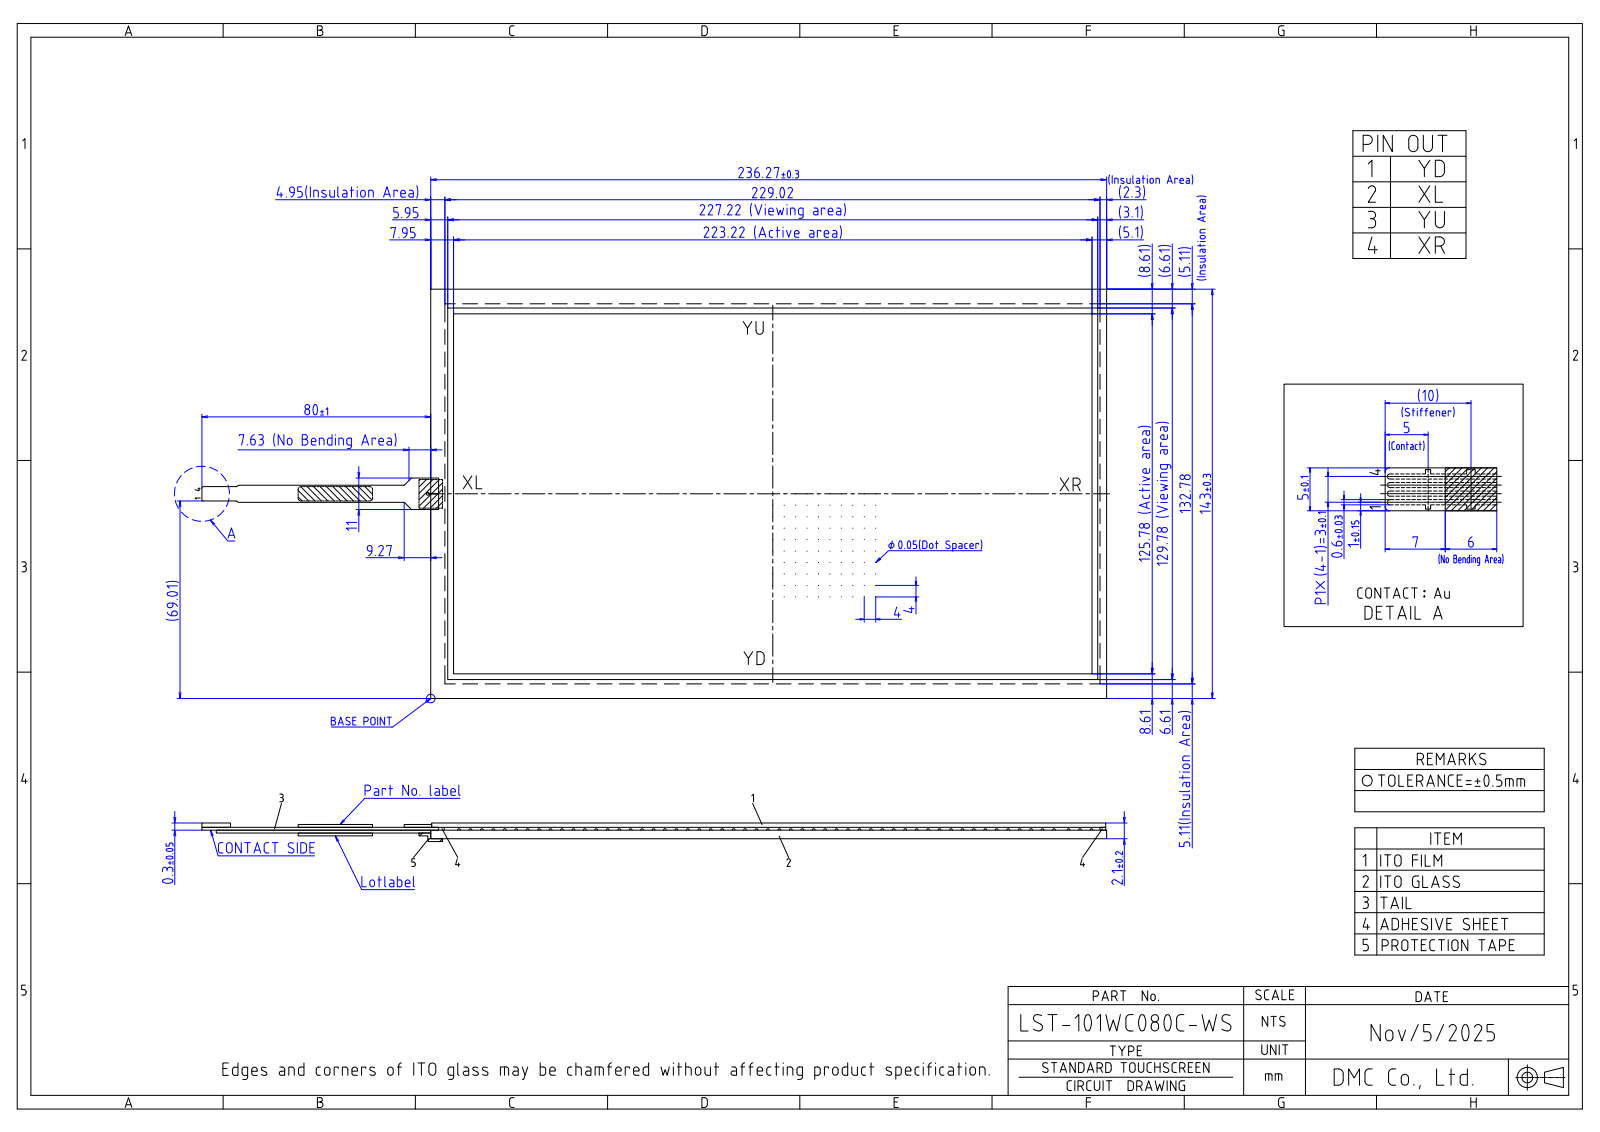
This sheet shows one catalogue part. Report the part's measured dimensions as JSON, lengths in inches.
{"part_name": "LST-101WC080C-WS (3Dデータ)", "step_written_by": "Autodesk Inventor 2024 (AUTOMOTIVE_DESIGN)", "units": "inches", "bodies": {"solids": 2, "faces": 52, "planar": 46, "cylindrical": 6, "other": 0}, "overall_size": [14.312, 7.882, 0.102], "volume_in3": 4.325, "surface_area_in2": 109, "partial_cylinders_radius": [[0.012, 4], [0.02, 2]], "face_to_face_distances": [0.083, 0.079, 5.63, 0.087, 0.091, 9.302, 0.02, 0.024, 0.016, 0.102]}
